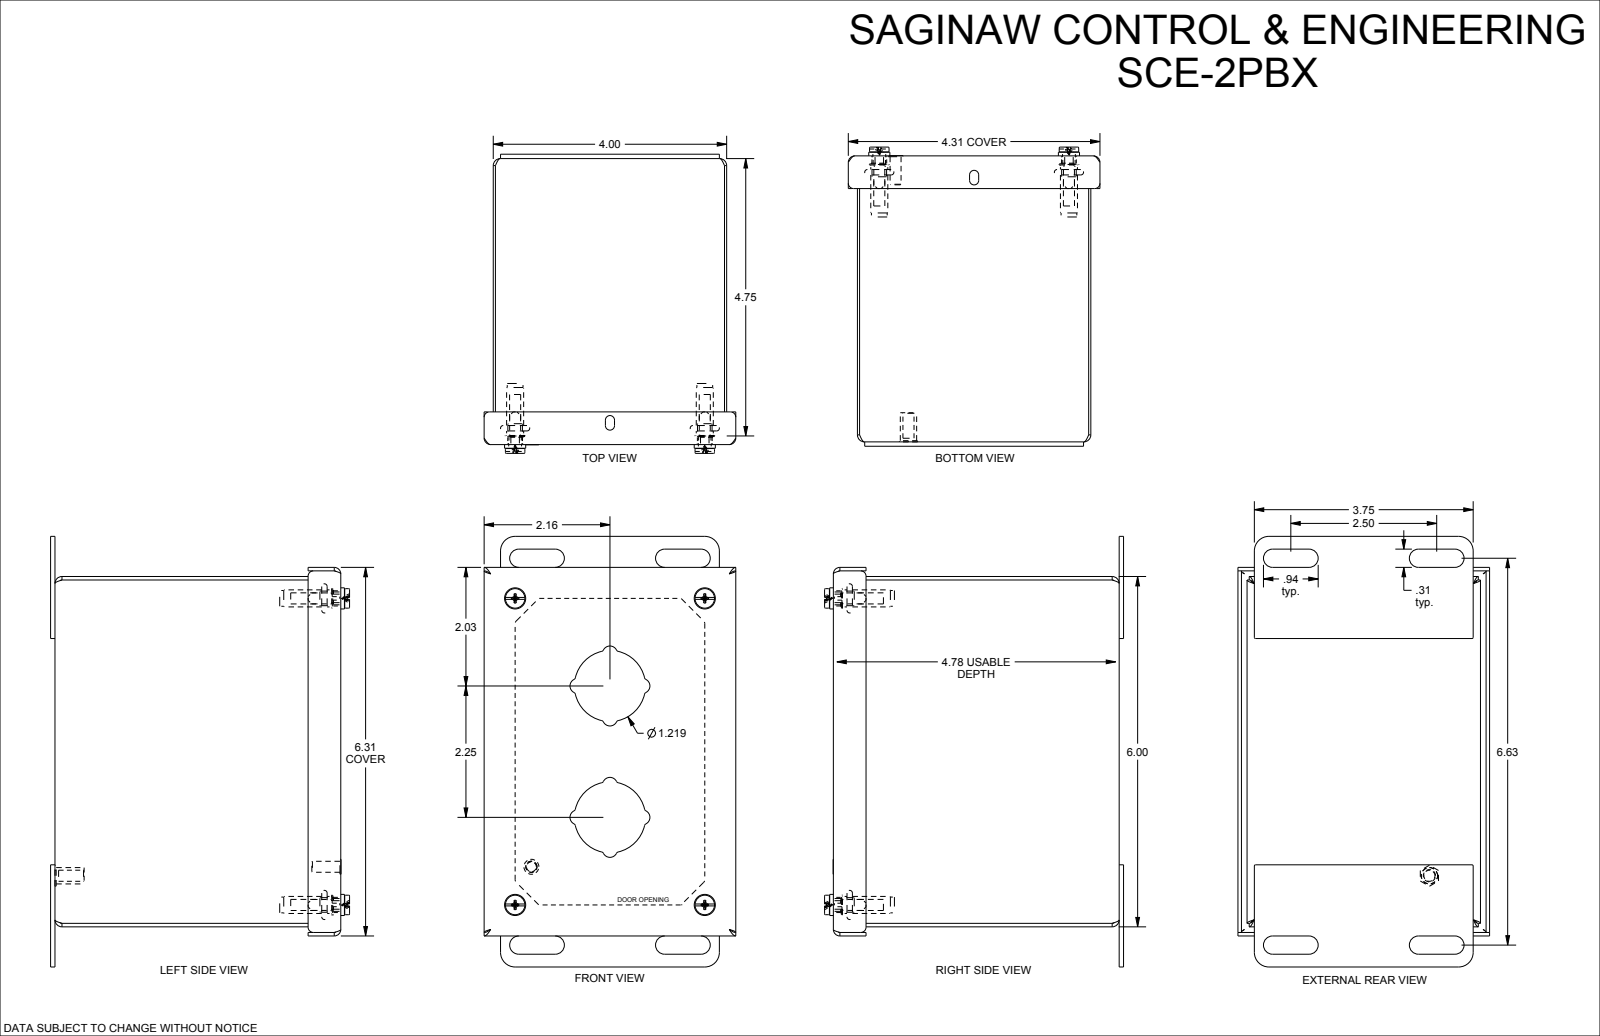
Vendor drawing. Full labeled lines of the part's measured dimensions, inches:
Part name (STEP PRODUCT): SCE-2PBX-RAL1018
STEP written by: SolidWorks 2021 (AUTOMOTIVE_DESIGN)
Units: inches
Bodies: 19 solids, 567 faces (209 planar, 188 cylindrical, 170 other)
Overall size (bounding box): 7.375 × 5.124 × 4.32
Volume: 11.02 in³ · Surface area: 366.2 in²
Round holes (diameter × count): ⌀0.19 ×5, ⌀0.22 ×4, ⌀0.25 ×4, ⌀0.266 ×4, ⌀0.317 ×4
Round bosses / shafts (diameter × count): ⌀0.188 ×5, ⌀0.437 ×4, ⌀0.362 ×4, ⌀0.34 ×4, ⌀0.334 ×4, ⌀0.292 ×4, ⌀0.27 ×4, ⌀0.26 ×4
Partial cylindrical surfaces — rounded edges, fillets, slot ends (radius × count): R0.06 ×20, R0.04 ×16, R0.015 ×8, R0.063 ×8, R0.115 ×8, R0.125 ×8, R0.156 ×8, R0.245 ×8
Main face-to-face distances: 0.06, 3.94, 4.838, 5.94, 4, 3.88, 4.898, 4.778, 6, 5.88
Hole centre spacings: 5.25, 3.25, 5.247, 6.175, 3.25, 3.258, 5.25, 6.174
